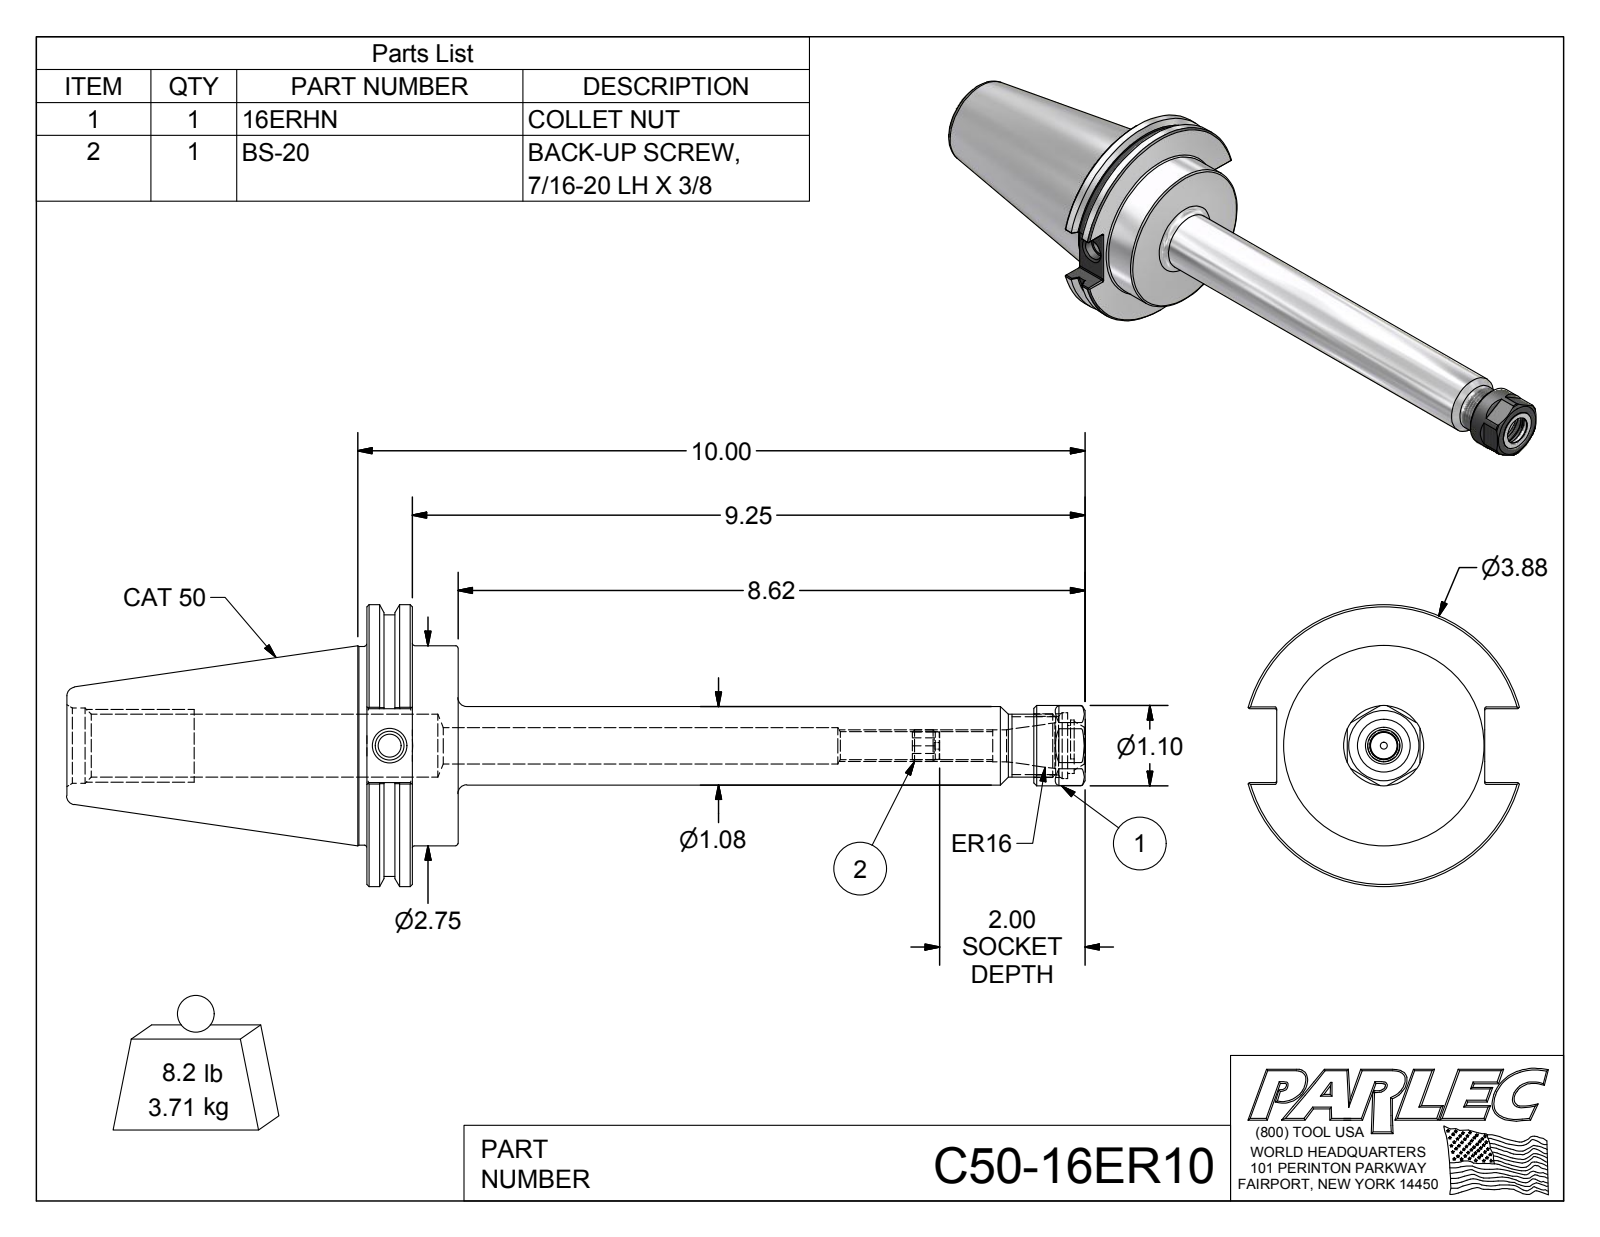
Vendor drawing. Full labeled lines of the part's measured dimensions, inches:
Part name (STEP PRODUCT): C50-16ER10; C50-16ER10-1; 16ERHN; BS-20
STEP written by: Autodesk Inventor 2012 (AUTOMOTIVE_DESIGN)
Units: inches
Bodies: 3 solids, 146 faces (60 planar, 39 cylindrical, 47 other)
Overall size (bounding box): 14.005 × 3.875 × 3.729
Volume: 29.03 in³ · Surface area: 121 in²
Round holes (diameter × count): ⌀0.09 ×1, ⌀0.315 ×1, ⌀0.383 ×1, ⌀0.399 ×1, ⌀0.44 ×1, ⌀0.5 ×1, ⌀0.508 ×1, ⌀0.661 ×1, ⌀0.807 ×1, ⌀0.865 ×1, ⌀0.906 ×1, ⌀1.038 ×1
Round bosses / shafts (diameter × count): ⌀3.875 ×1, ⌀3.594 ×1, ⌀2.75 ×1, ⌀2.73 ×1, ⌀1.102 ×1, ⌀1.08 ×1, ⌀0.866 ×1, ⌀0.724 ×1
Partial cylindrical surfaces — rounded edges, fillets, slot ends (radius × count): R0.02 ×12, R0.354 ×1
Main face-to-face distances: 1.255, 0.625, 0.63, 9.25, 0.236, 4.125, 4.75, 5.38, 1, 2.86
Hole centre spacings: 0.051
